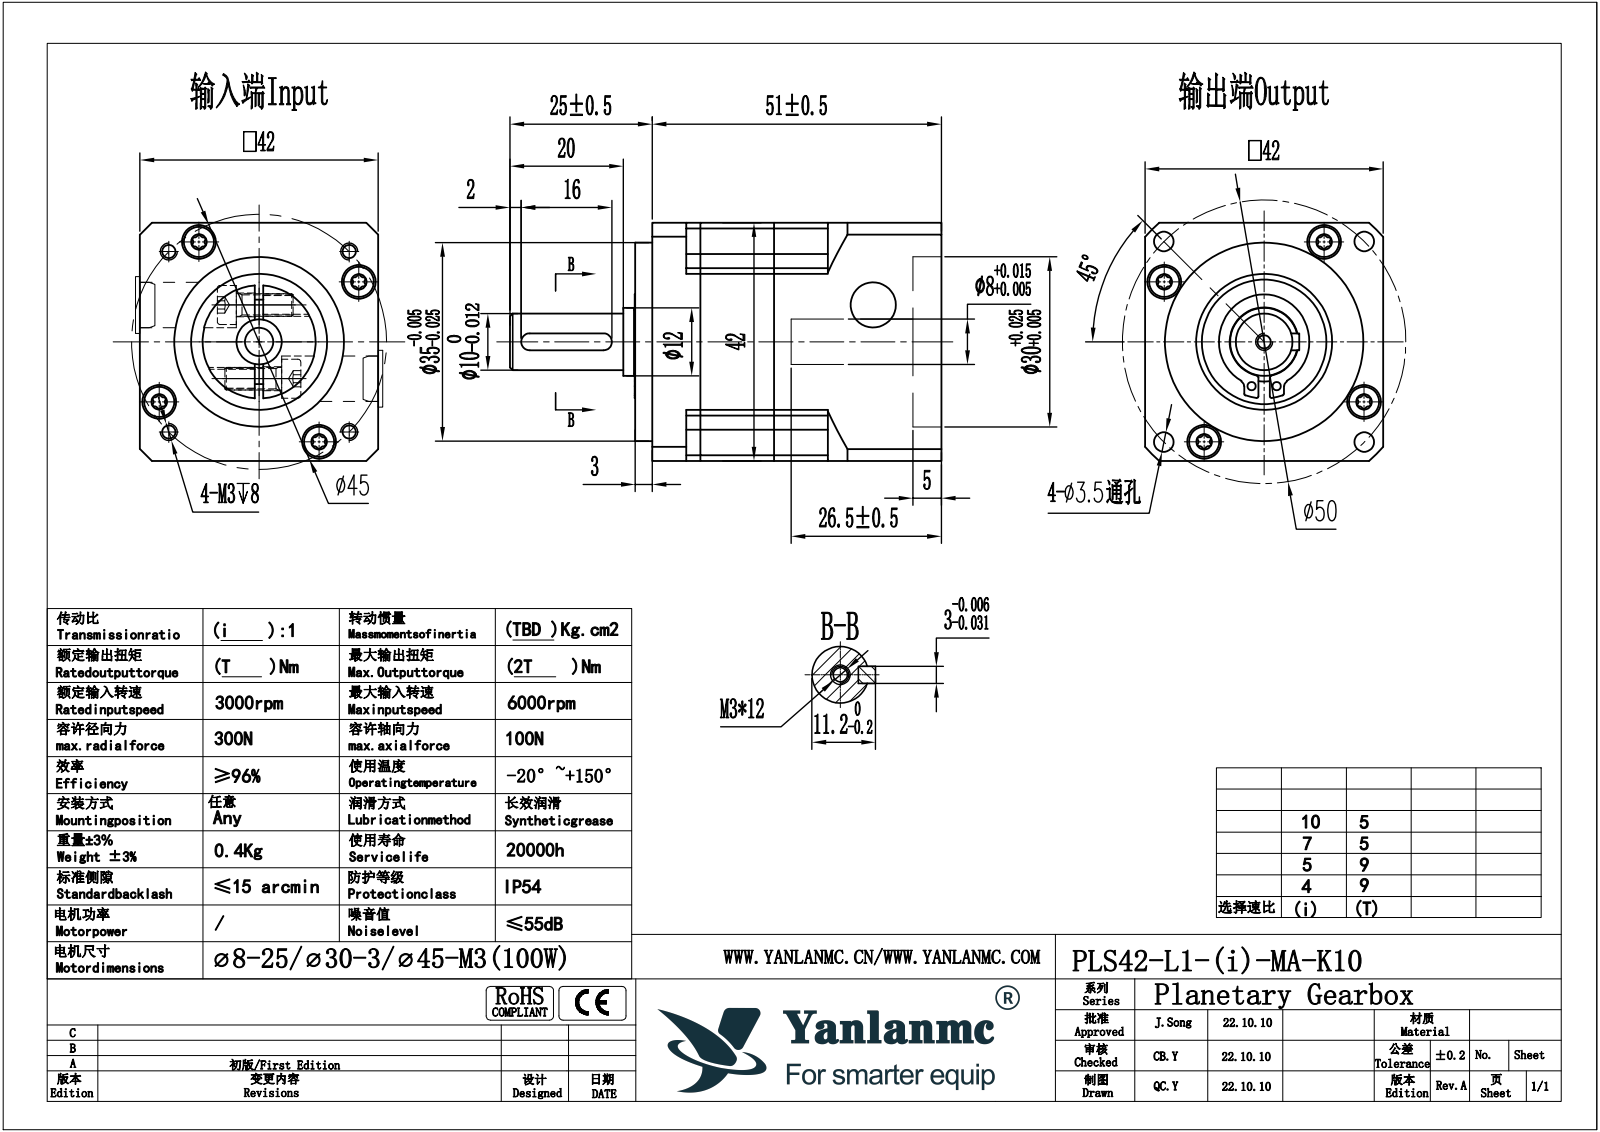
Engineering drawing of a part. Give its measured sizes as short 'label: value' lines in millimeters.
name: 6901RS.IGS; PS42-L1MA.IGS; ABF42-NN.IGS; SS输入轴.IGS (+1 more)
written by: SolidWorks 2020 (CONFIG_CONTROL_DESIGN)
unit: mm
bodies: 10 solids, 461 faces (0 planar, 0 cylindrical, 461 other)
size: 76.1 × 42 × 42
volume: 47 024 mm³; area: 32 929 mm²
